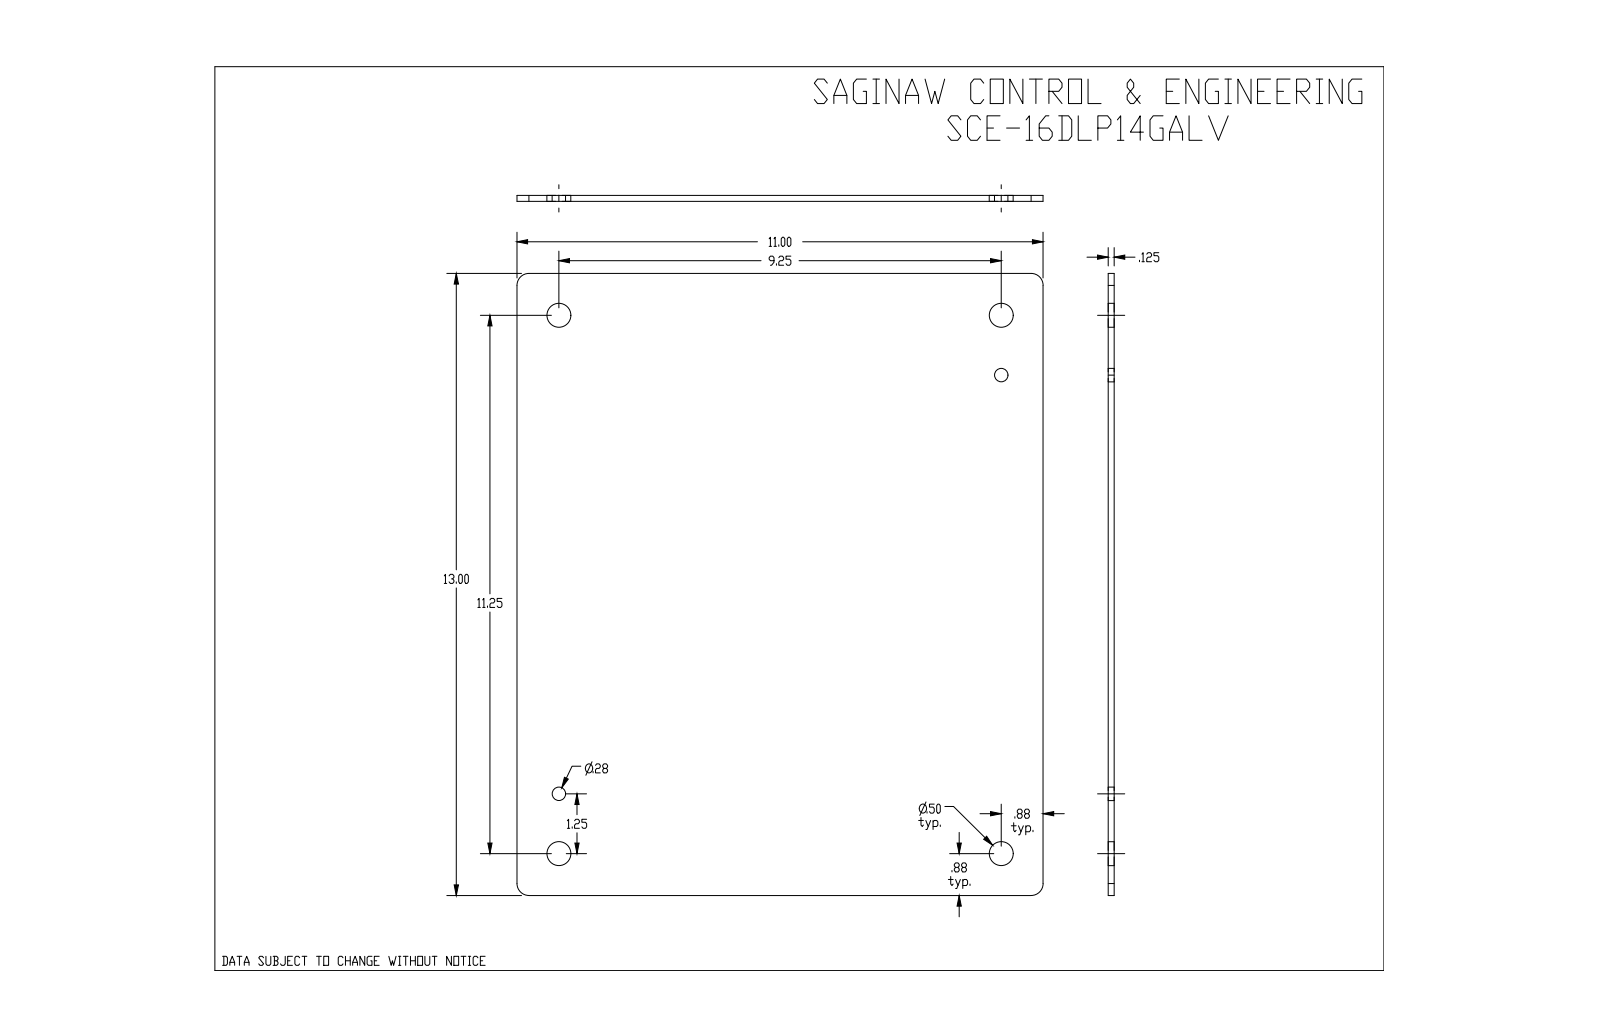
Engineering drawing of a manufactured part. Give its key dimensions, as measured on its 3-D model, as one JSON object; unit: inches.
{"part_name": "SCE-16DLP14GALV", "step_written_by": "SolidWorks 2019 (CONFIG_CONTROL_DESIGN)", "units": "inches", "bodies": {"solids": 1, "faces": 16, "planar": 6, "cylindrical": 10, "other": 0}, "overall_size": [13, 11, 0.125], "volume_in3": 17.75, "surface_area_in2": 291, "round_holes": [[0.5, 4], [0.281, 1], [0.281, 1]], "partial_cylinders_radius": [[0.25, 4]], "face_to_face_distances": [0.125, 11, 13], "hole_center_spacings": [1.25, 9.25, 9.334, 10, 11.25, 13.622, 14.565, 12.732]}
